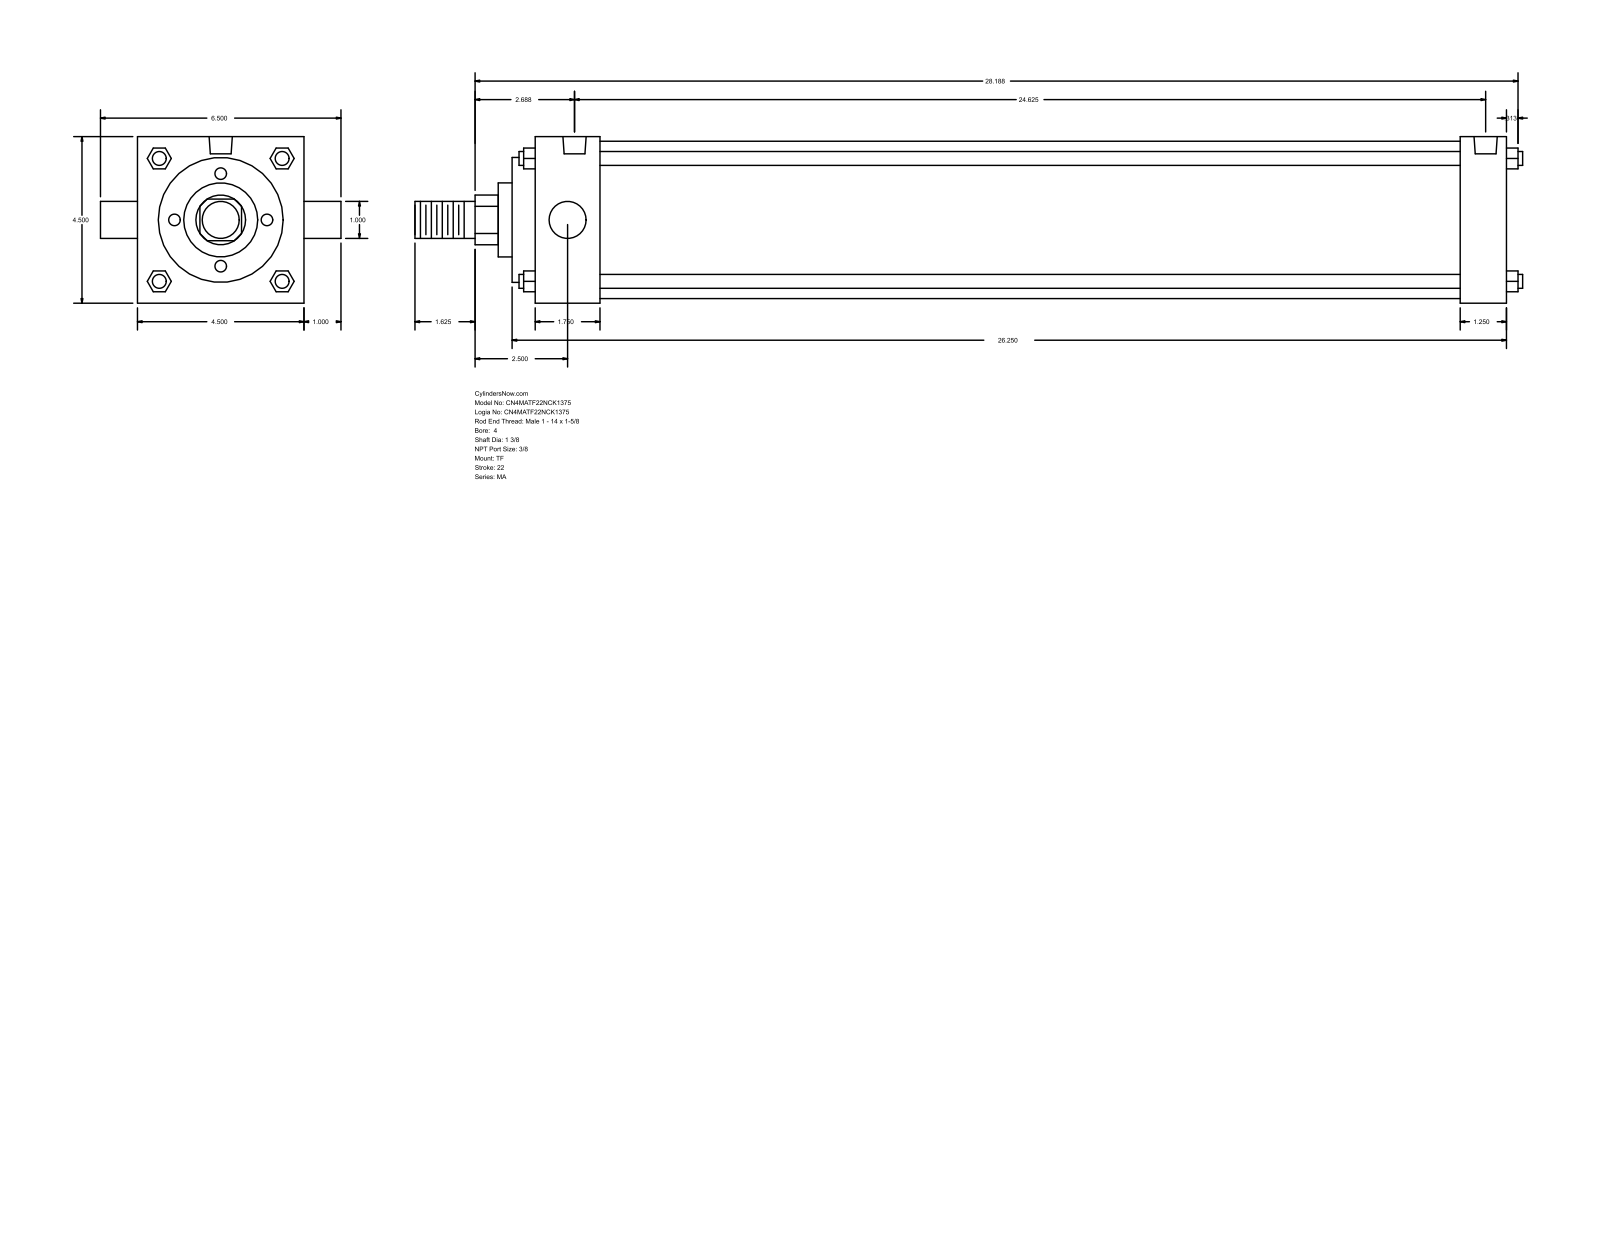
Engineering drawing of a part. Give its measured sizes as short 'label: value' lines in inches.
name: MA_TF__0400_1.375
written by: GSSL Pune (CONFIG_CONTROL_DESIGN)
unit: in
bodies: 0 solids, 122 faces (93 planar, 29 cylindrical, 0 other)
size: 29.937 × 6.5 × 4.5
holes: 3× ⌀0.437, 2× ⌀0.627
bosses: 4× ⌀0.375, 2× ⌀1, 1× ⌀4.25, 1× ⌀3.375, 1× ⌀2, 1× ⌀1.375
rounds: 1× R0.672
face distances: 4.5, 26.25, 26.875, 0.625, 25.625, 25, 1.25, 2.375, 1.75, 23.25
hole spacings: 0.187, 0.188, 24.25, 24.437, 24.438, 24.625
